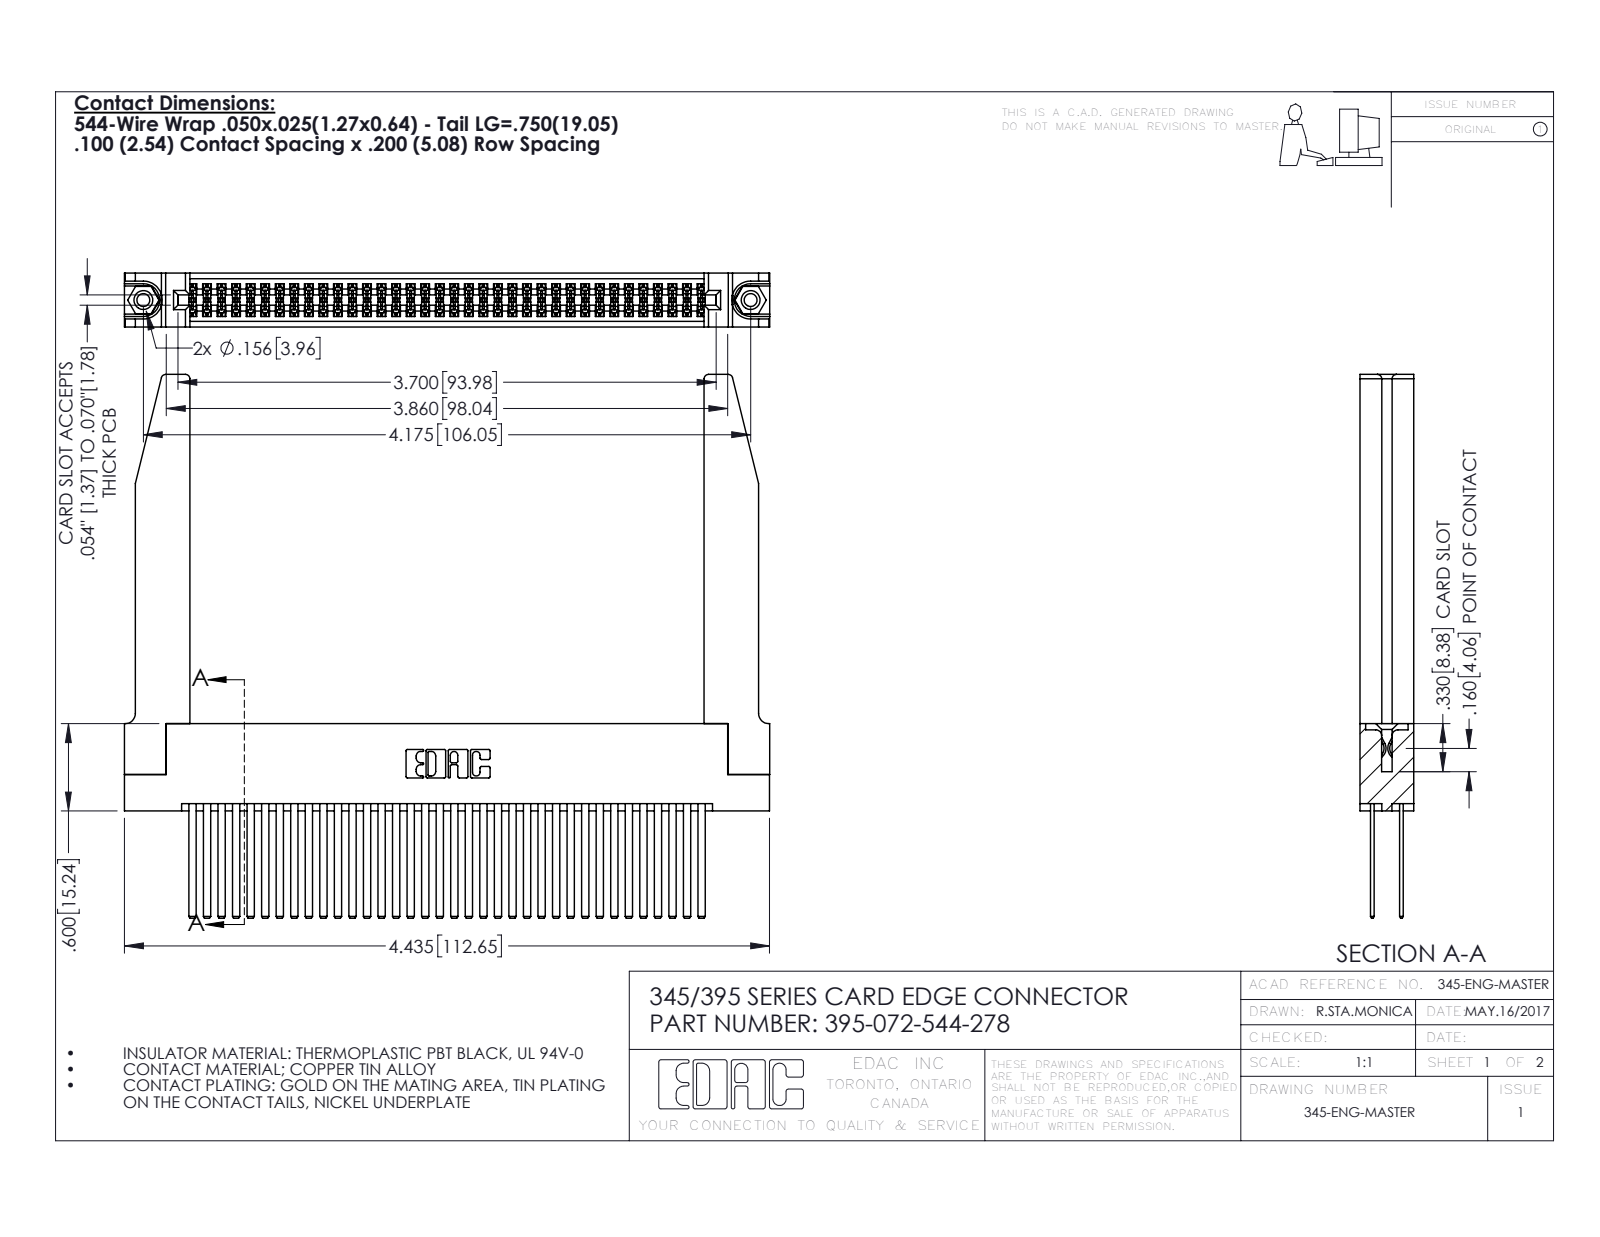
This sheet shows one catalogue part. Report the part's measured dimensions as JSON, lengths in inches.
{"part_name": "345-250-001_345-250-001-102; 395-072-544-278; 345-220-078_345-220-078; 345-292-001_345-293-144 (+1 more)", "step_written_by": "SolidWorks 2016 (CONFIG_CONTROL_DESIGN)", "units": "inches", "bodies": {"solids": 77, "faces": 3528, "planar": 2310, "cylindrical": 1166, "other": 52}, "overall_size": [4.436, 3.737, 0.37], "volume_in3": 1.2, "surface_area_in2": 42.27, "round_holes": [[0.089, 2], [0.125, 2], [0.156, 2], [0.064, 1]], "round_bosses_or_shafts": [[0.155, 2]], "partial_cylinders_radius": [[0.006, 108], [0.01, 22], [0.03, 8], [0.007, 6], [0.031, 6], [0.026, 3], [0.014, 2], [0.019, 2]], "face_to_face_distances": [0.072, 0.298, 0.2, 0.098, 0.272, 0.025, 0.37, 0.225, 0.175, 0.148], "hole_center_spacings": [0.27, 3.939, 4.175]}
